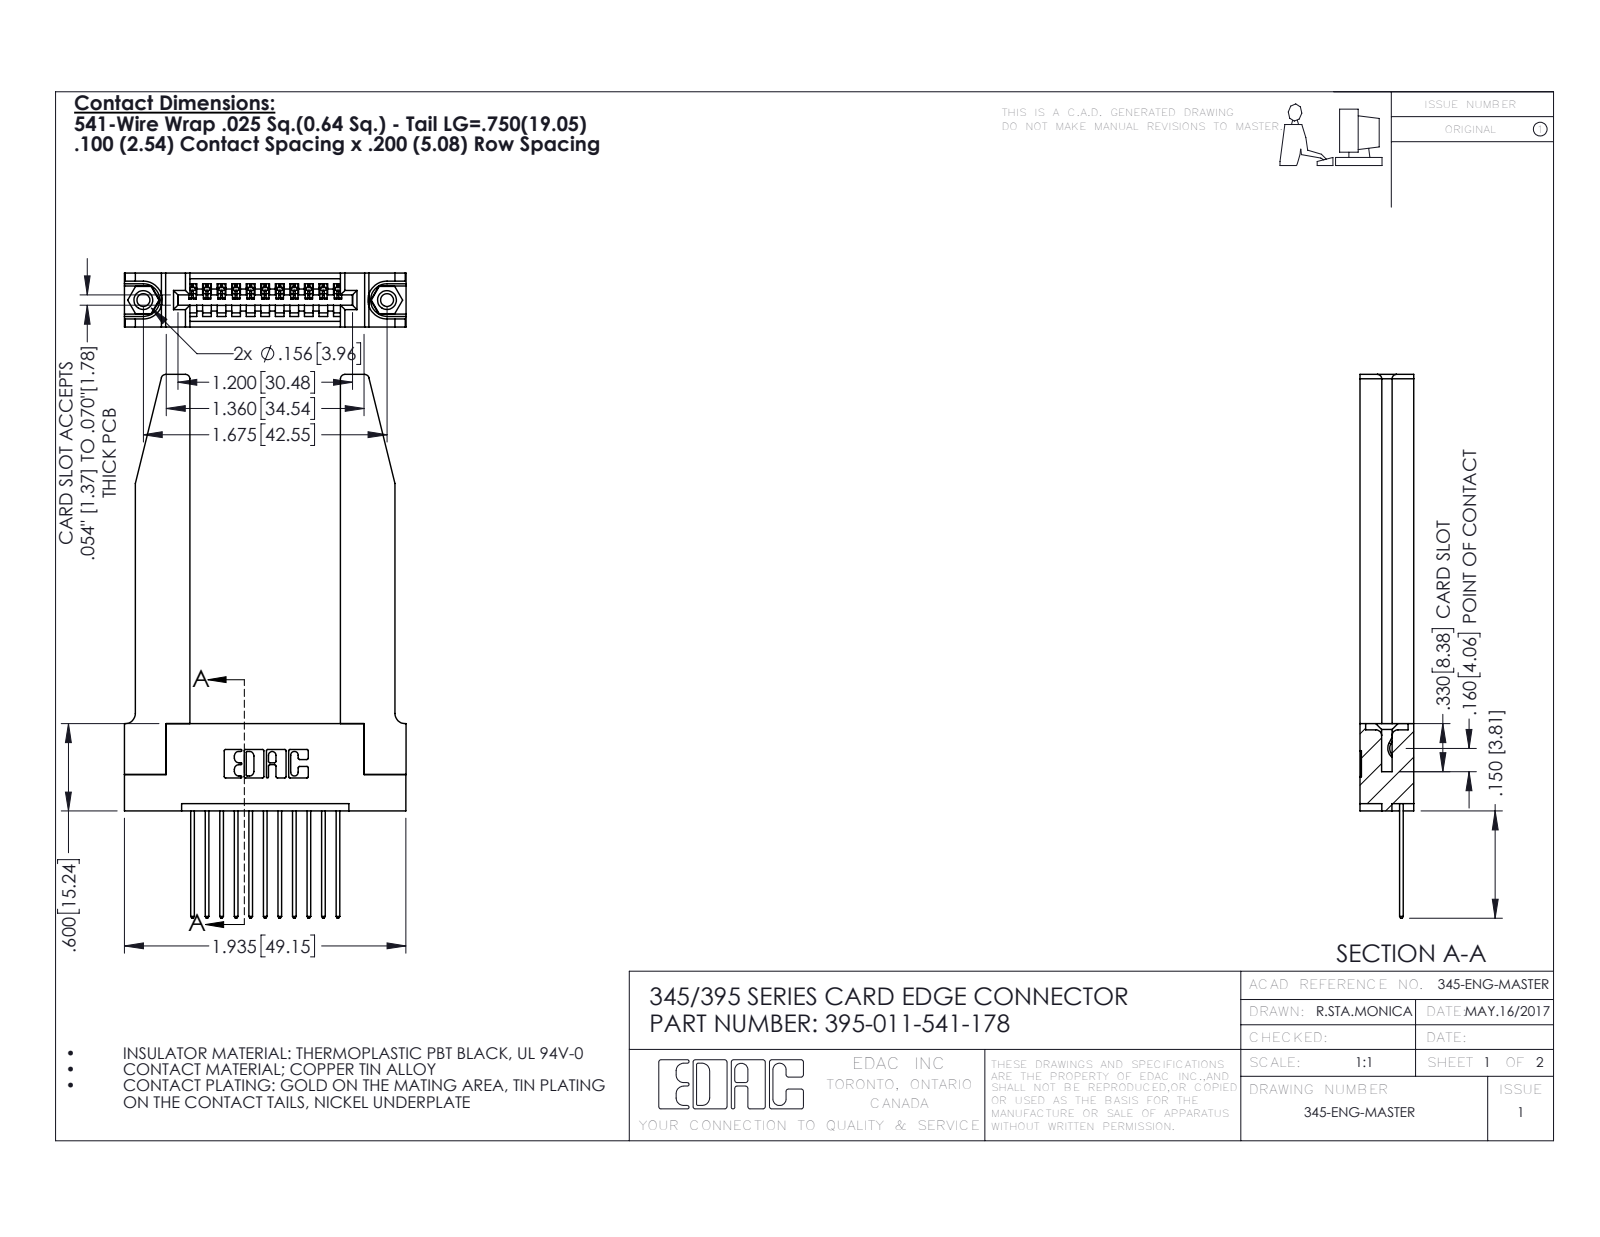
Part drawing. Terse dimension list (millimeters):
name: 345 Part_Flush Mounting Lugs - 0.156 Dia-TH; 345-250-001_345-250-001-102; 345-220-078_345-220-078; 395-011-541-178 (+1 more)
written by: SolidWorks 2016 (CONFIG_CONTROL_DESIGN)
unit: mm
bodies: 16 solids, 998 faces (662 planar, 284 cylindrical, 52 other)
size: 94.9 × 49.2 × 9.4
volume: 12 200 mm³; area: 12 550 mm²
holes: 2× ⌀2.3, 2× ⌀3.2, 2× ⌀4, 1× ⌀1.6
bosses: 2× ⌀3.9
rounds: 22× R0.2, 22× R0.3, 22× R0.3, 8× R0.8, 6× R0.2, 6× R0.8, 3× R0.7, 2× R0.8
face distances: 9.4, 1.8, 7.6, 5.1, 3.8, 3.8, 2, 5.6, 26.3, 2.5
hole spacings: 6.9, 36.7, 42.5
